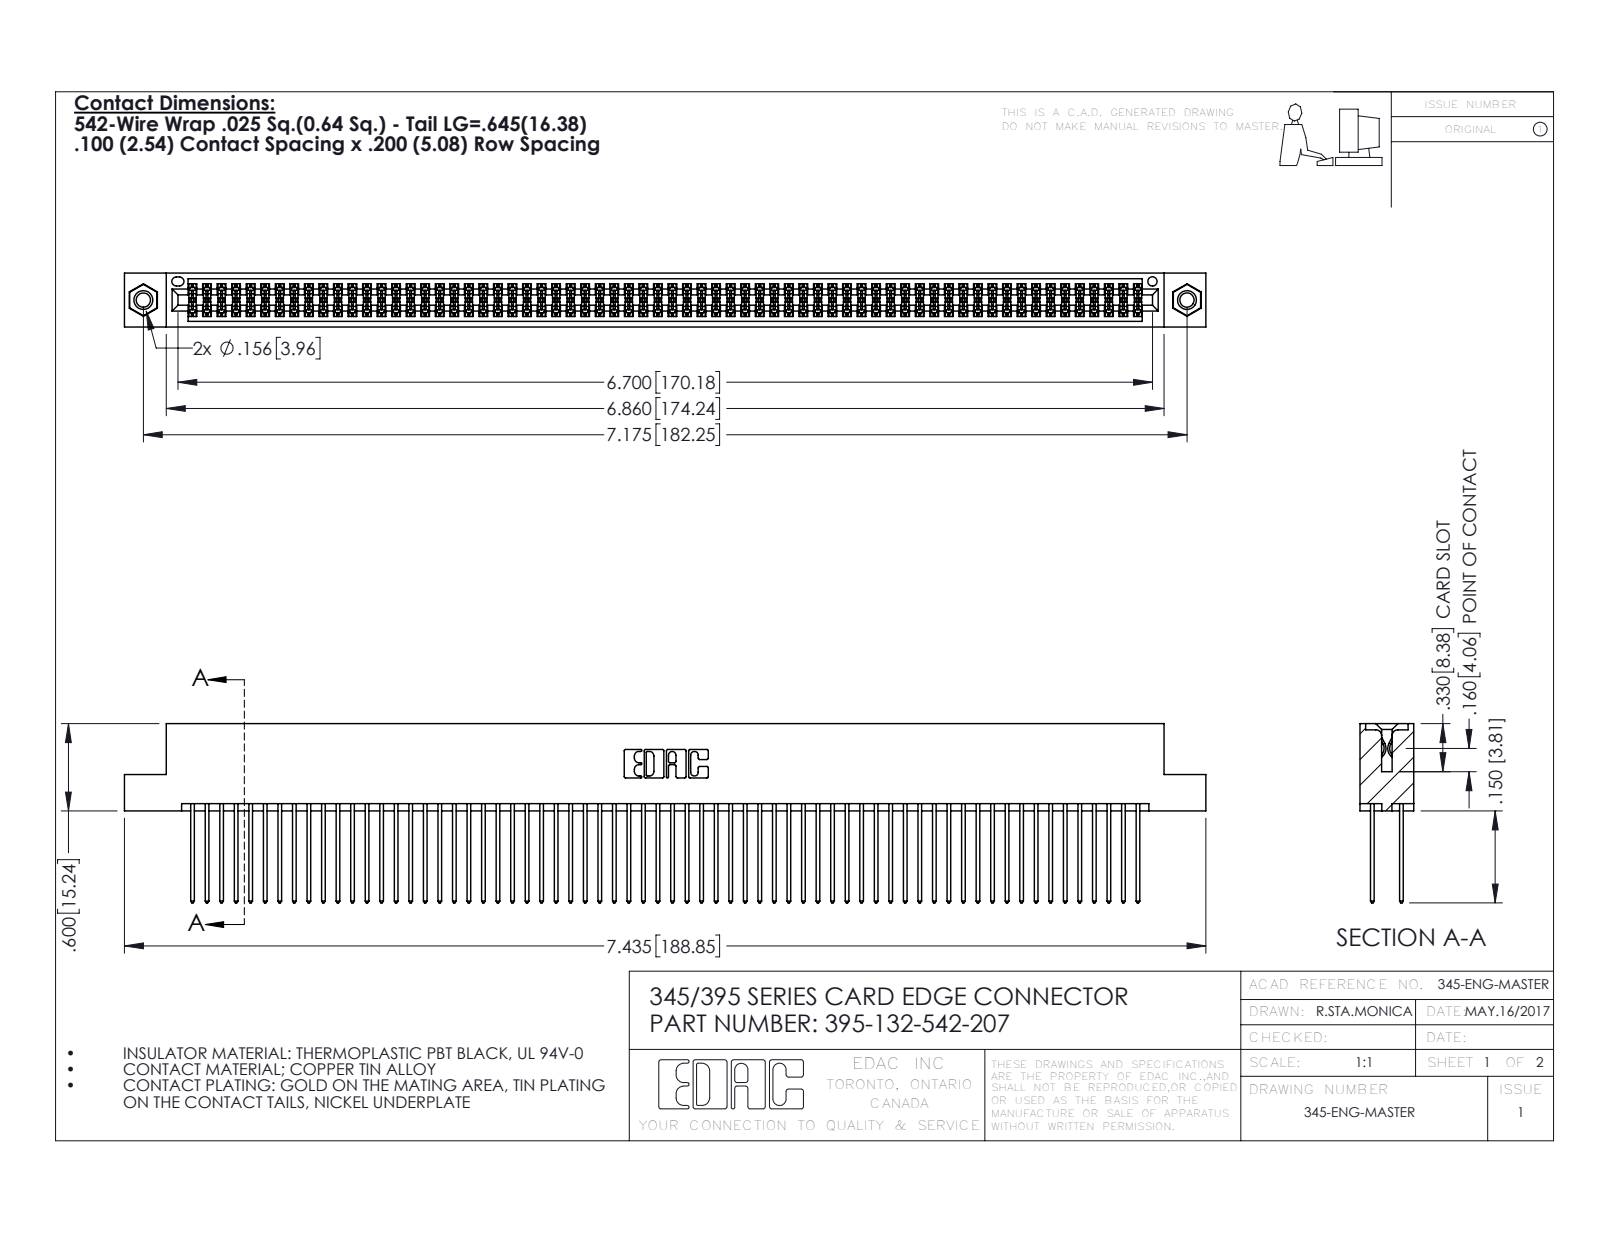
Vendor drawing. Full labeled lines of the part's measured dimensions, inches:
Part name (STEP PRODUCT): 345-292-001_345-293-142; 345-250-001_345-250-005-103; 395-132-542-207; 345 Part_Flush Mounting Lugs - 0.156 Dia-TI
STEP written by: SolidWorks 2016 (CONFIG_CONTROL_DESIGN)
Units: inches
Bodies: 135 solids, 6786 faces (4468 planar, 2302 cylindrical, 16 other)
Overall size (bounding box): 7.435 × 1.232 × 0.37
Volume: 1.17 in³ · Surface area: 49.14 in²
Round holes (diameter × count): ⌀0.098 ×2, ⌀0.125 ×2, ⌀0.156 ×2, ⌀0.064 ×1
Round bosses / shafts (diameter × count): ⌀0.155 ×2
Partial cylindrical surfaces — rounded edges, fillets, slot ends (radius × count): R0.006 ×198, R0.01 ×132, R0.01 ×22, R0.007 ×6, R0.031 ×6, R0.026 ×3, R0.014 ×2, R0.019 ×2
Main face-to-face distances: 0.072, 0.298, 0.2, 0.098, 0.272, 0.025, 0.225, 0.37, 0.175, 0.149
Hole centre spacings: 0.27, 6.939, 7.175
